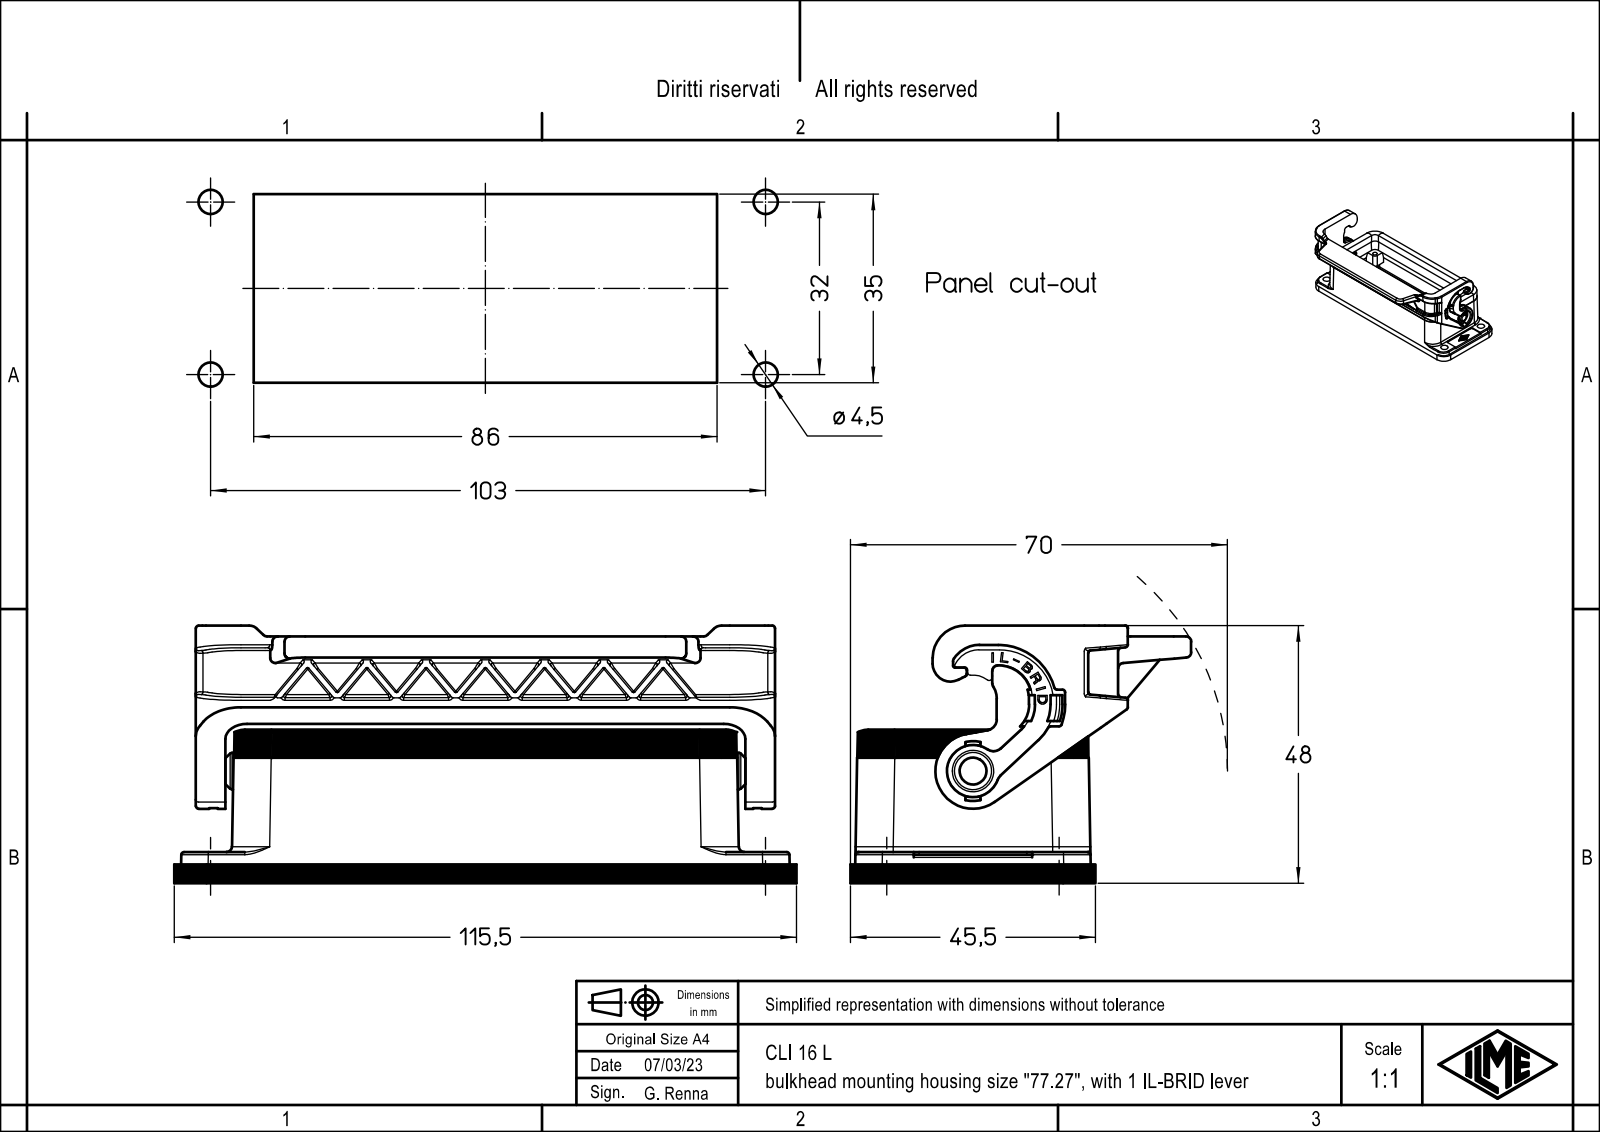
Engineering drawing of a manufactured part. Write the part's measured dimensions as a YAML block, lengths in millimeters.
part_name: "CLI 16 L"
step_written_by: "Creo Elements/Direct Modeling 20.1B 02-Apr-2019 (C) Parametric Technology GmbH (AUTOMOTIVE_DESIGN)"
units: millimeters
bodies: {solids: 1, faces: 1033, planar: 667, cylindrical: 280, other: 86}
overall_size: [115.5, 63.25, 47.8]
volume: 48867
surface_area: 32789
round_holes:
  - {diameter: 3.8, count: 4}
  - {diameter: 4.5, count: 4}
  - {diameter: 3.25, count: 1}
  - {diameter: 5.4, count: 1}
  - {diameter: 7.7, count: 1}
round_bosses_or_shafts:
  - {diameter: 6.9, count: 1}
  - {diameter: 6.8, count: 1}
  - {diameter: 5.2, count: 1}
  - {diameter: 3.2, count: 1}
partial_cylinders:
  - {radius: 0.1, count: 27}
  - {radius: 1, count: 21}
  - {radius: 0.17, count: 15}
  - {radius: 0.2, count: 15}
  - {radius: 2, count: 13}
  - {radius: 4, count: 12}
  - {radius: 0.5, count: 11}
  - {radius: 7, count: 10}
face_to_face_distances: [3.03, 45.8, 5.5, 40.5, 102, 96.5, 3.5, 38.9, 38.96, 35.93]
hole_center_spacings: [32, 103, 107.86]
